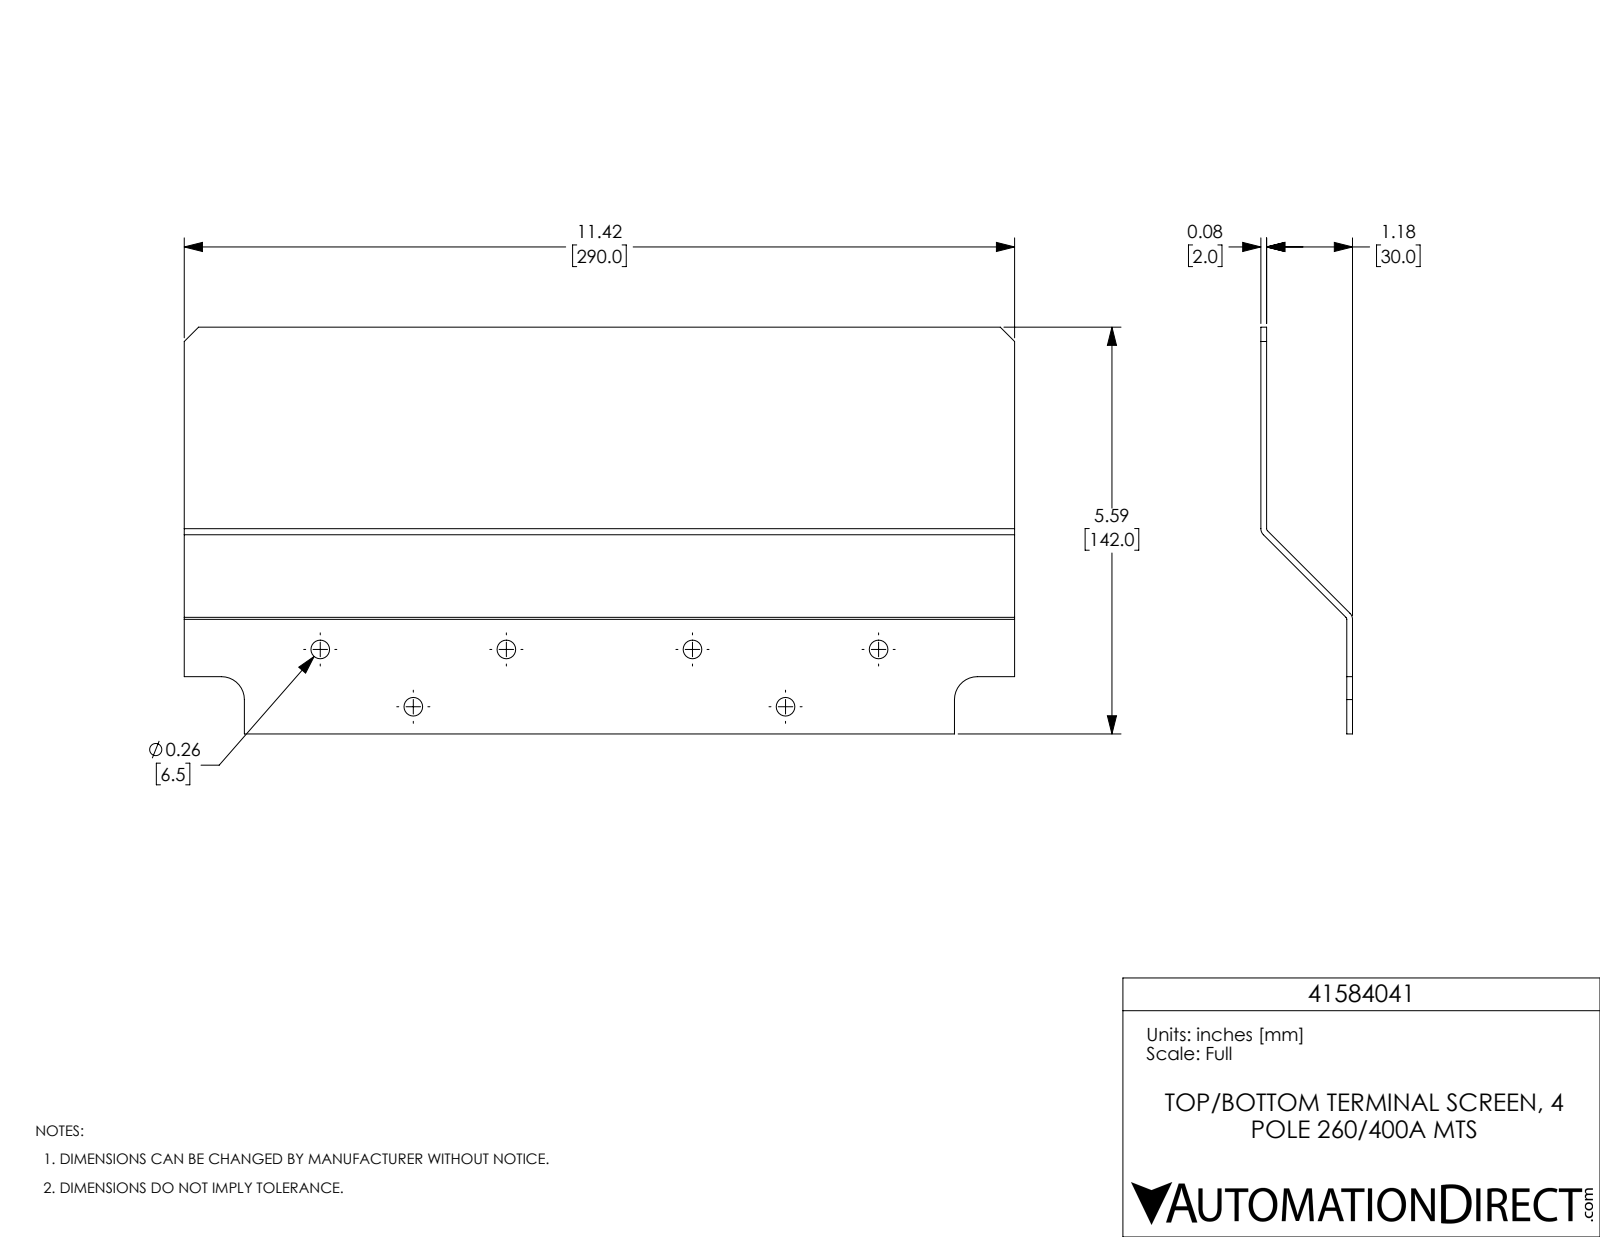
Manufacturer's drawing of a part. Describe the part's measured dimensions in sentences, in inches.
The part is named "41584041". Its 3-D file was written by "SolidWorks 2017 (AUTOMOTIVE_DESIGN)". It is 1 solid with 34 faces: 16 planar, 18 cylindrical and 0 other. Overall it measures 11.417 by 5.591 by 1.26 inches. Its volume is 5.333 cubic inches and its surface area 138.6 square inches. Round holes: 6 of diameter 0.256. Partial cylindrical surfaces (rounded edges, fillets, slot ends): 2 of radius 0.039, 2 of radius 0.118, 2 of radius 0.315. The main face-to-face distances are 0.079, 1.181, 1.102, 1.26, 5.591, 11.417, 0.787, 4.803, 0.827, 10.591. The hole center spacings are 1.502, 2.559, 5.118, 3.919, 6.446, 7.677.
